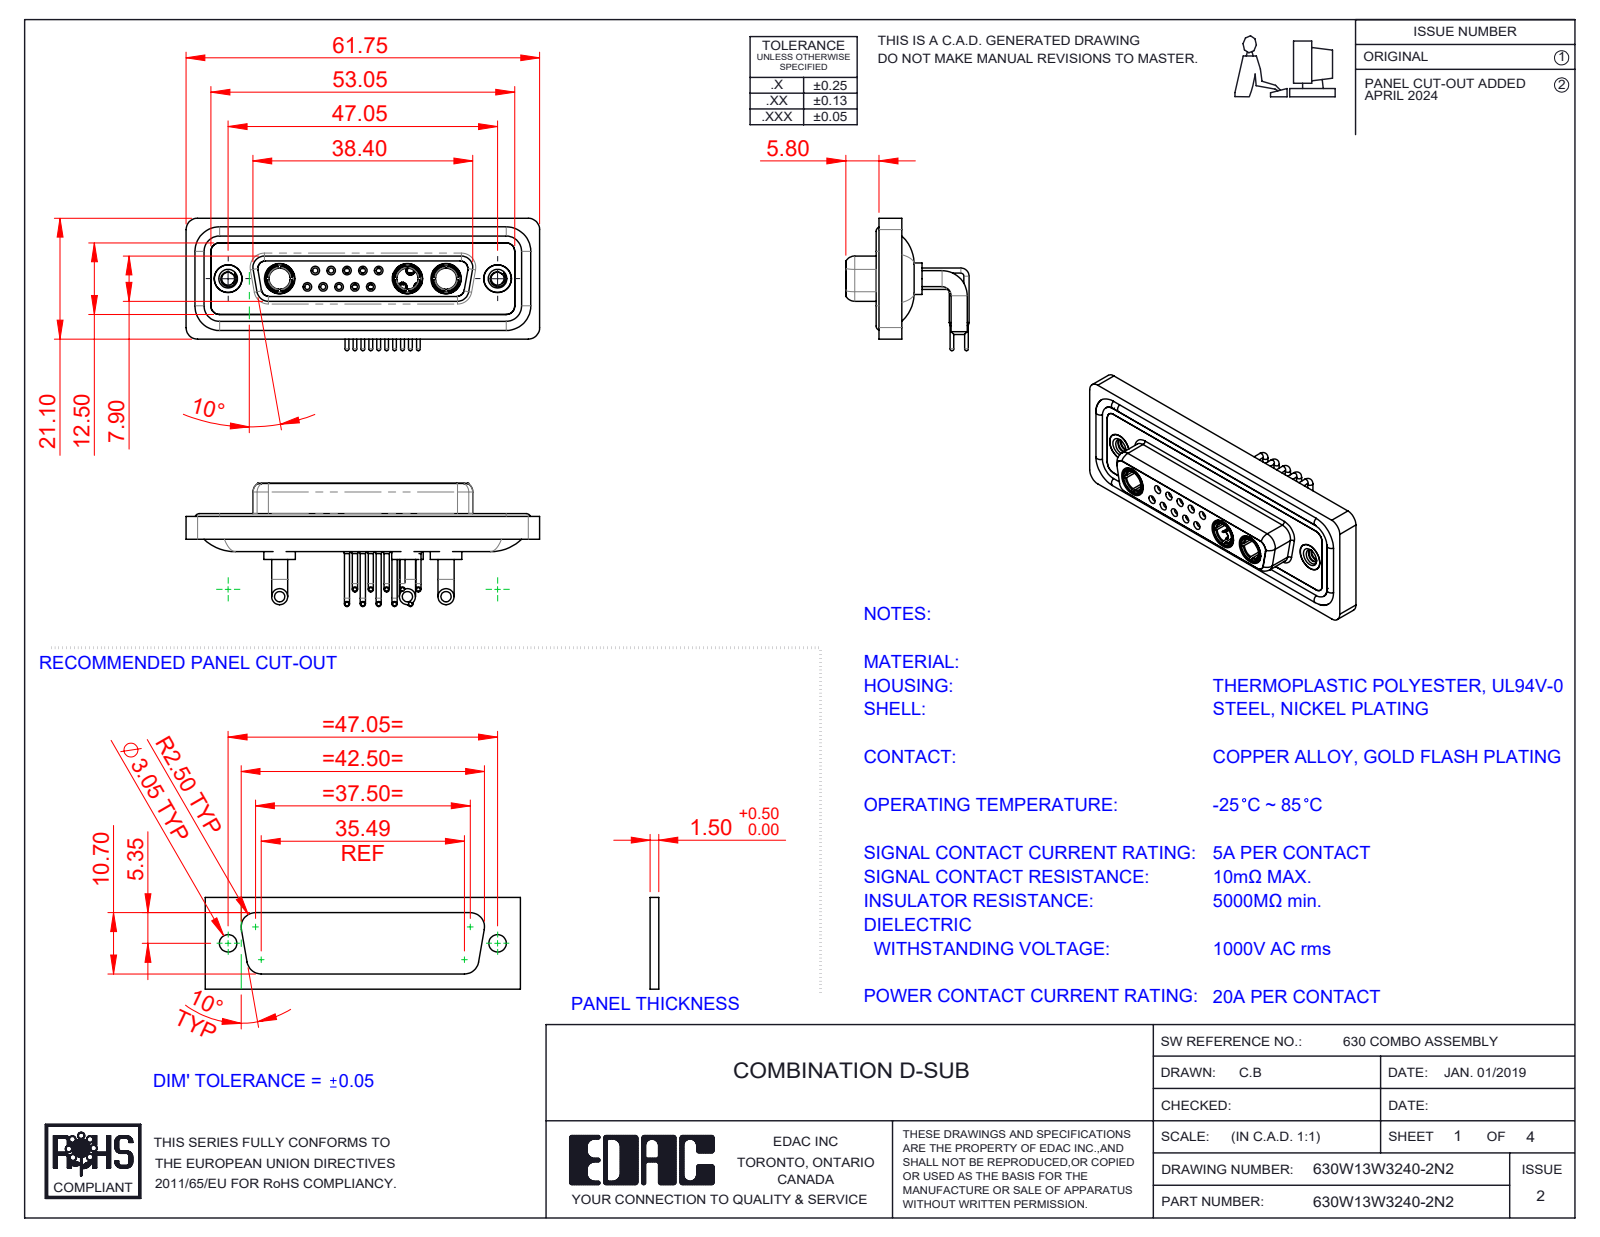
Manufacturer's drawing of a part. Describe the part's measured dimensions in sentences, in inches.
The part is named "630Combo Contact Row 2_50 Contacts; 630Combo Waterproof Housing_25 Contacts; 630Combo Threaded Rivet_2; 630W13W3240-2N2 (+5 more)". Its 3-D file was written by "SolidWorks 2023 (CONFIG_CONTROL_DESIGN)". It is 23 solids with 1150 faces: 342 planar, 493 cylindrical and 315 other. Overall it measures 2.431 by 0.91 by 0.848 inches. Its volume is 0.517 cubic inches and its surface area 22.16 square inches. Round holes: 10 of diameter 0.035, 10 of diameter 0.043, 10 of diameter 0.059, 10 of diameter 0.079, 5 of diameter 0.063, 5 of diameter 0.067, 5 of diameter 0.191, 3 of diameter 0.146, 3 of diameter 0.209, 2 of diameter 0.089, 2 of diameter 0.157, 2 of diameter 0.159. Round bosses or shafts: 15 of diameter 0.035, 12 of diameter 0.063, 10 of diameter 0.026, 6 of diameter 0.11, 5 of diameter 0.079, 5 of diameter 0.059, 3 of diameter 0.217, 3 of diameter 0.205. Partial cylindrical surfaces (rounded edges, fillets, slot ends): 18 of radius 0.059, 18 of radius 0.079, 8 of radius 0.053, 8 of radius 0.063, 4 of radius 0.01, 4 of radius 0.02, 4 of radius 0.024, 4 of radius 0.026. The main face-to-face distances are 0.016, 0.071, 0.161, 0.043, 0.063, 0.059, 0.122, 0.098, 0.146, 0.055. The hole center spacings are 0.124, 0.109, 0.218, 0.198, 0.327, 0.198, 0.295, 0.436.
